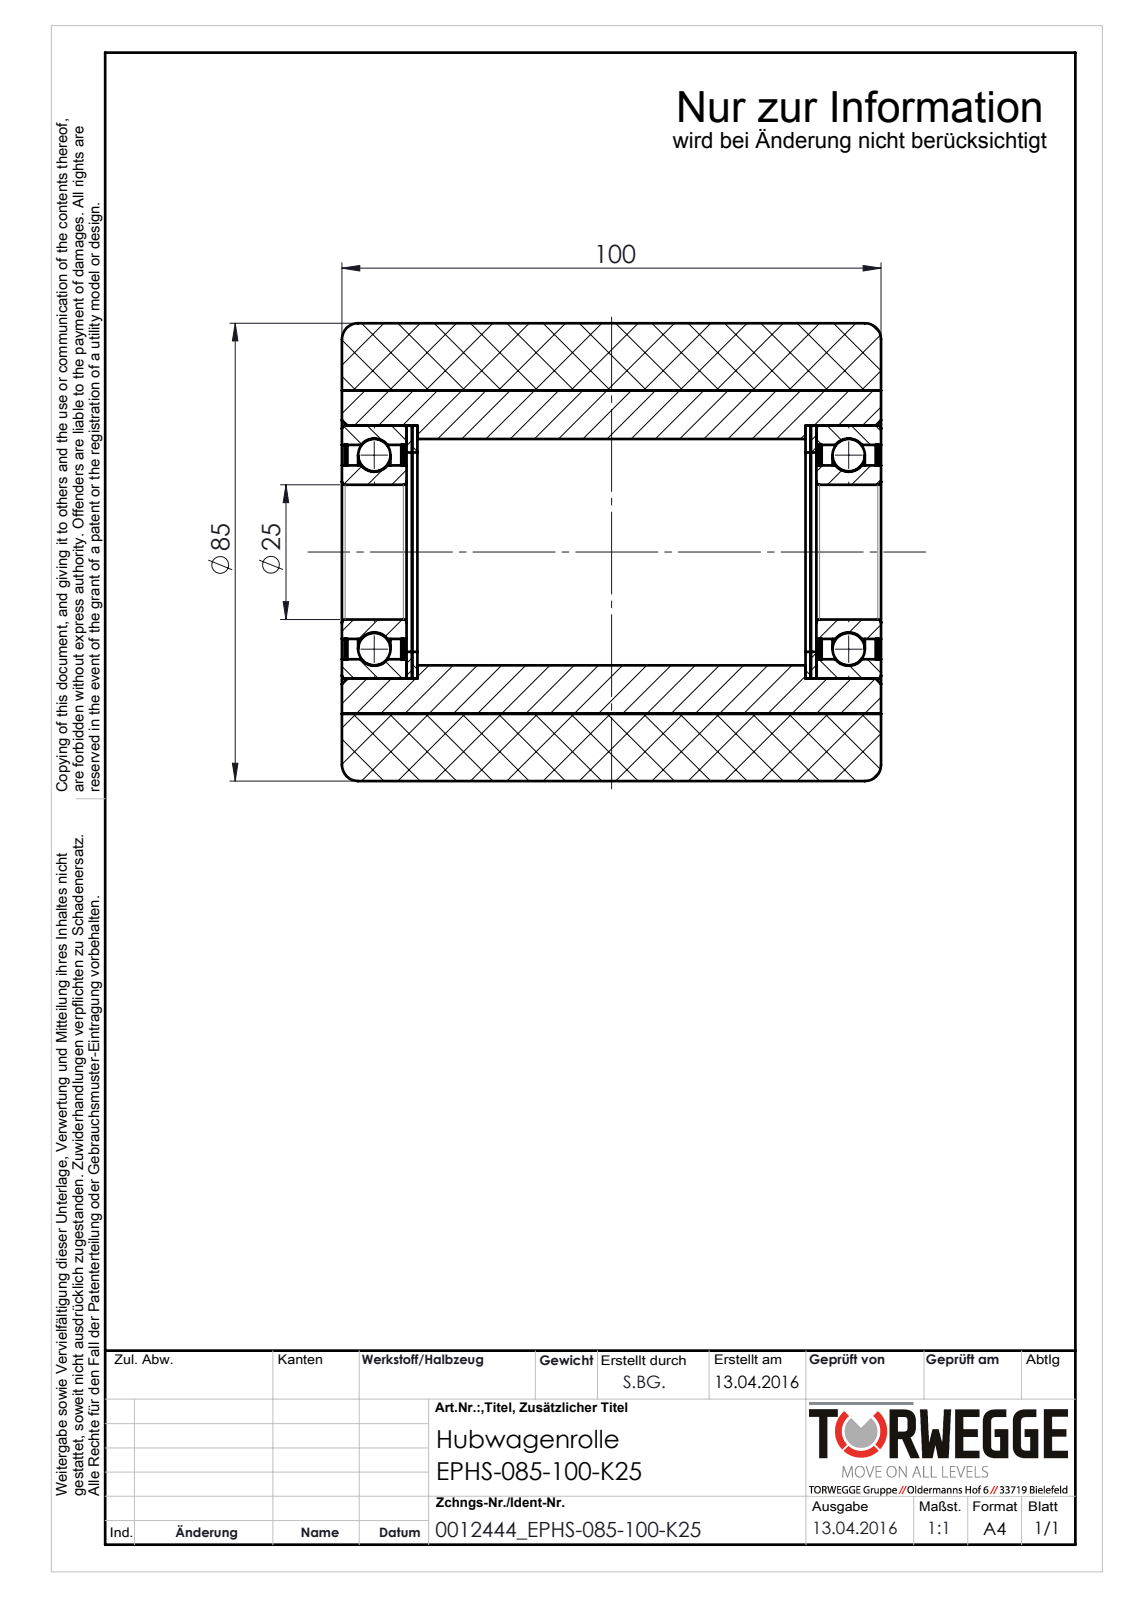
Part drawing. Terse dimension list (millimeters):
name: 0012444_EPHS-085-100-K25
written by: SolidWorks 2016 (AUTOMOTIVE_DESIGN)
unit: mm
bodies: 16 solids, 158 faces (30 planar, 68 cylindrical, 60 other)
size: 100 × 85 × 85
volume: 445 443 mm³; area: 114 319 mm²
holes: 1× ⌀25, 1× ⌀32.2, 1× ⌀37, 1× ⌀39.8, 1× ⌀42, 1× ⌀60
bosses: 1× ⌀85, 1× ⌀47
face distances: 1, 88, 100, 12, 0.5, 13, 87, 75, 74, 86
